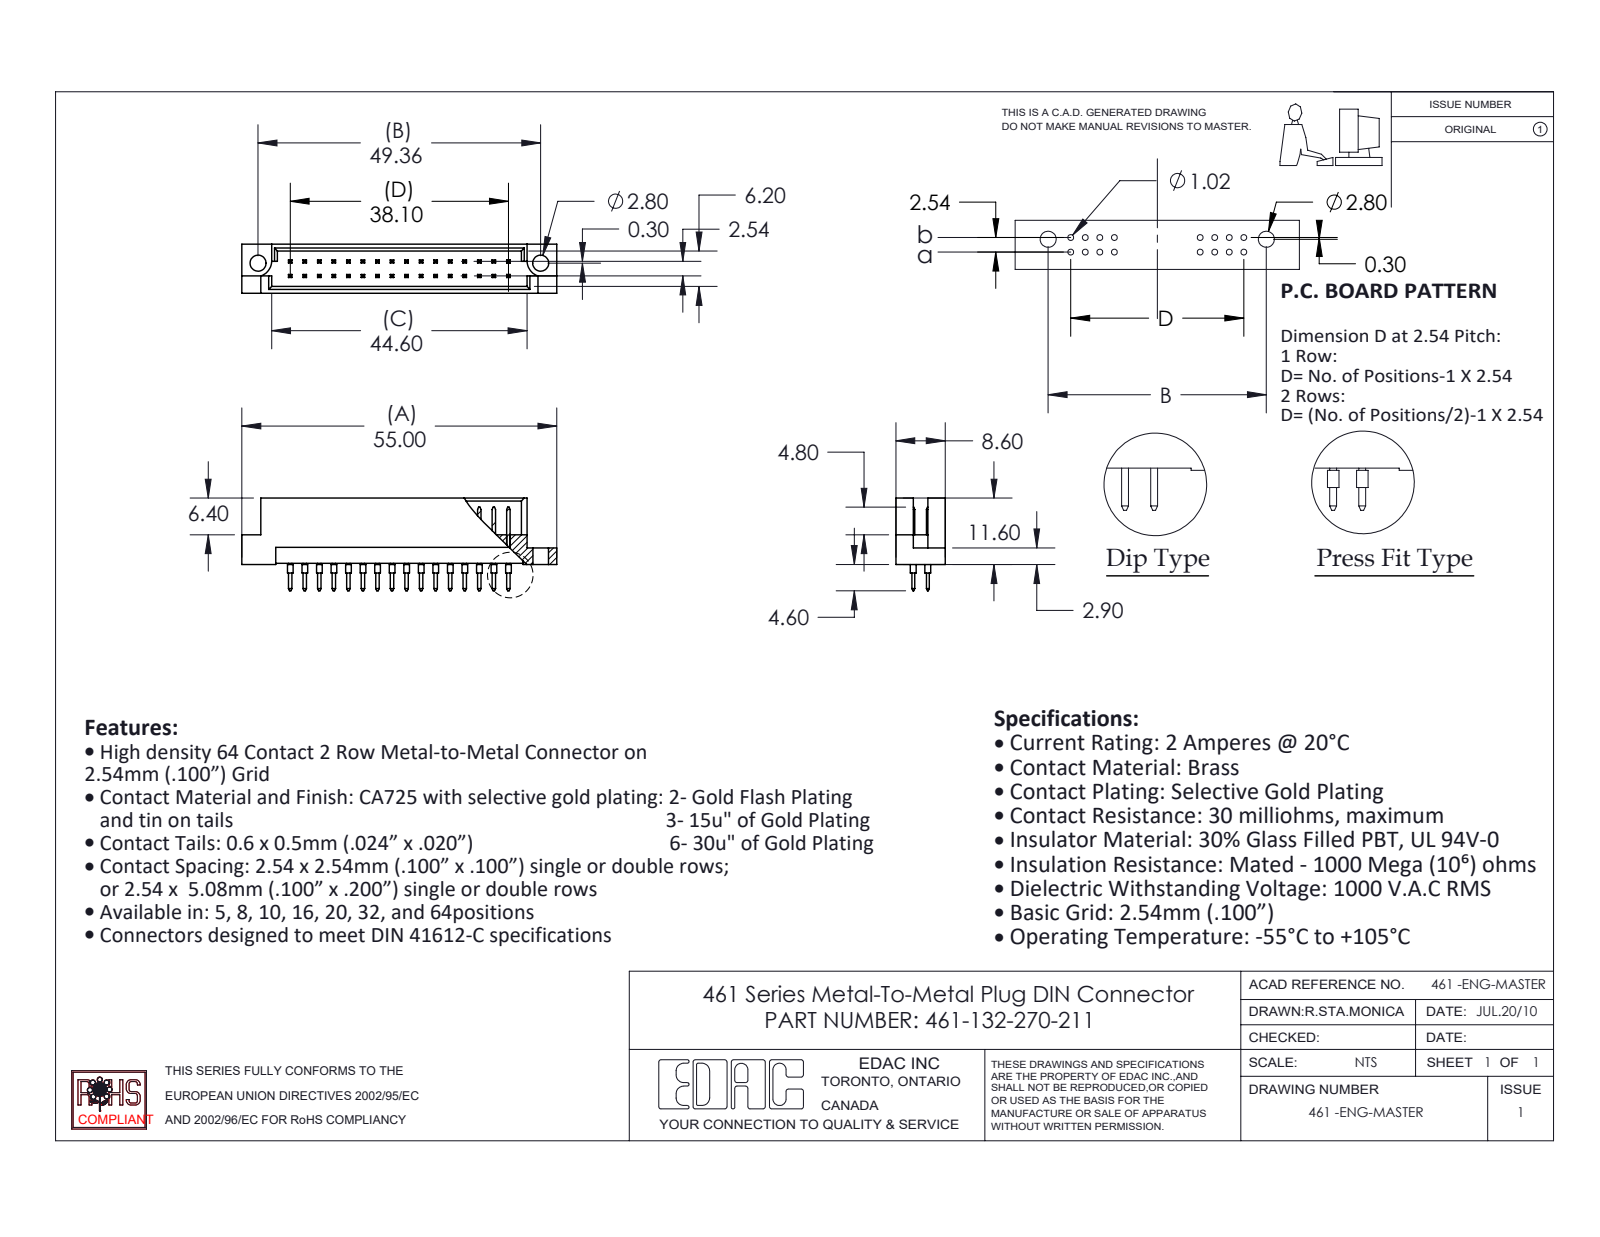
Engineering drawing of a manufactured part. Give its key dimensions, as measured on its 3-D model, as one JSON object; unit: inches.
{"part_name": "461 Part_32; 461-290_70; 461-132-270-211", "step_written_by": "SolidWorks 2020 (CONFIG_CONTROL_DESIGN)", "units": "inches", "bodies": {"solids": 33, "faces": 880, "planar": 810, "cylindrical": 70, "other": 0}, "overall_size": [2.165, 0.638, 0.339], "volume_in3": 0.172, "surface_area_in2": 6.725, "round_holes": [[0.11, 2]], "round_bosses_or_shafts": [[0.039, 32]], "partial_cylinders_radius": [[0.11, 2]], "face_to_face_distances": [0.047, 0.291, 0.1, 0.339, 0.244, 0.062, 0.109, 0.229, 0.182, 0.129], "hole_center_spacings": [1.943]}
